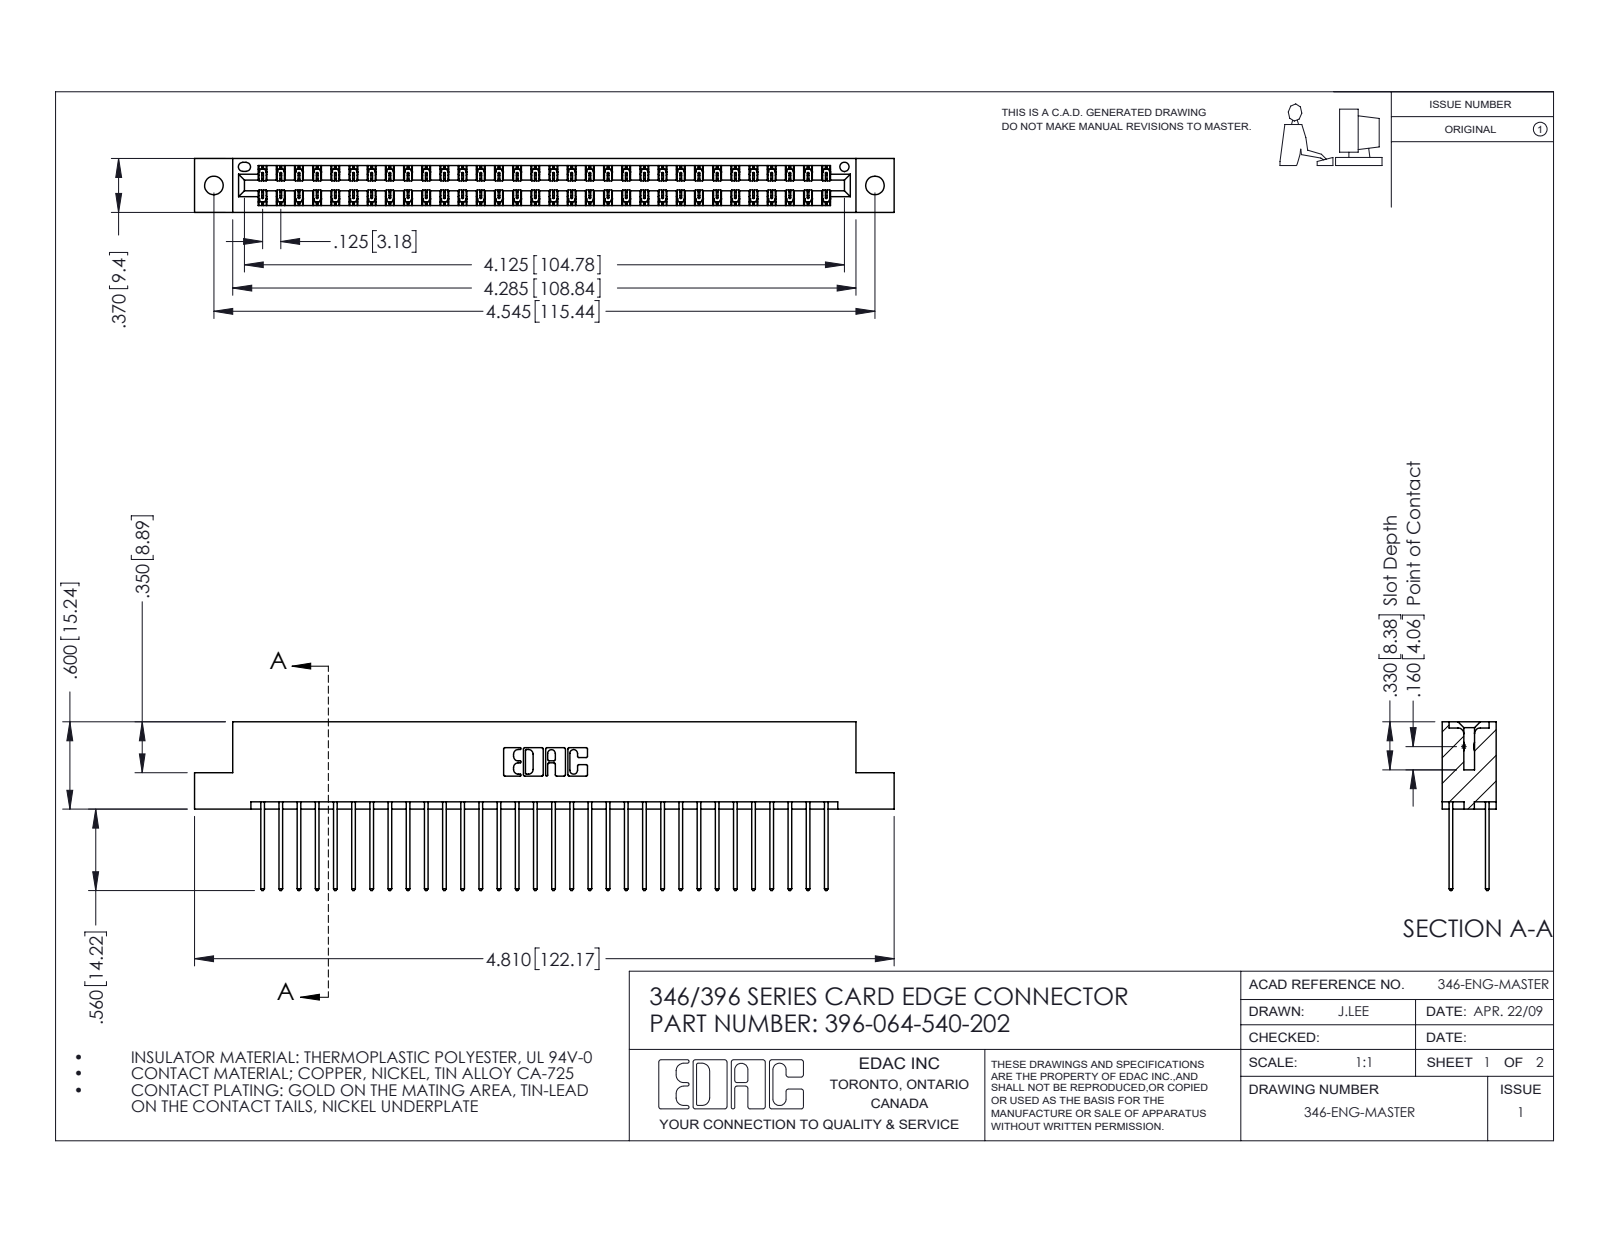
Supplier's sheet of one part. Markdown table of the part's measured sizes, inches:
| quantity | value |
| --- | --- |
| part name | 396-064-540-202; 345-292-001_345-293-140; 346 Part_Flush Mounting Lugs - 0.128 Dia |
| STEP written by | SolidWorks 2016 (CONFIG_CONTROL_DESIGN) |
| units | inches |
| bodies | 65 solids, 3450 faces (2316 planar, 1134 cylindrical, 0 other) |
| overall size | 4.81 × 1.16 × 0.37 |
| volume | 0.735 in³ |
| surface area | 26.77 in² |
| round holes (diameter × count) | 0.128 × 2, 0.064 × 1 |
| partial cylindrical surfaces (radius × count) | 0.006 × 96, 0.01 × 64, 0.01 × 22, 0.007 × 6, 0.031 × 6, 0.026 × 3, 0.014 × 2, 0.022 × 2 |
| main face-to-face distances | 0.048, 0.322, 0.25, 0.072, 0.298, 0.025, 0.37, 0.275, 0.148, 0.222 |
| hole center spacings | 0.246, 4.337, 4.545 |
